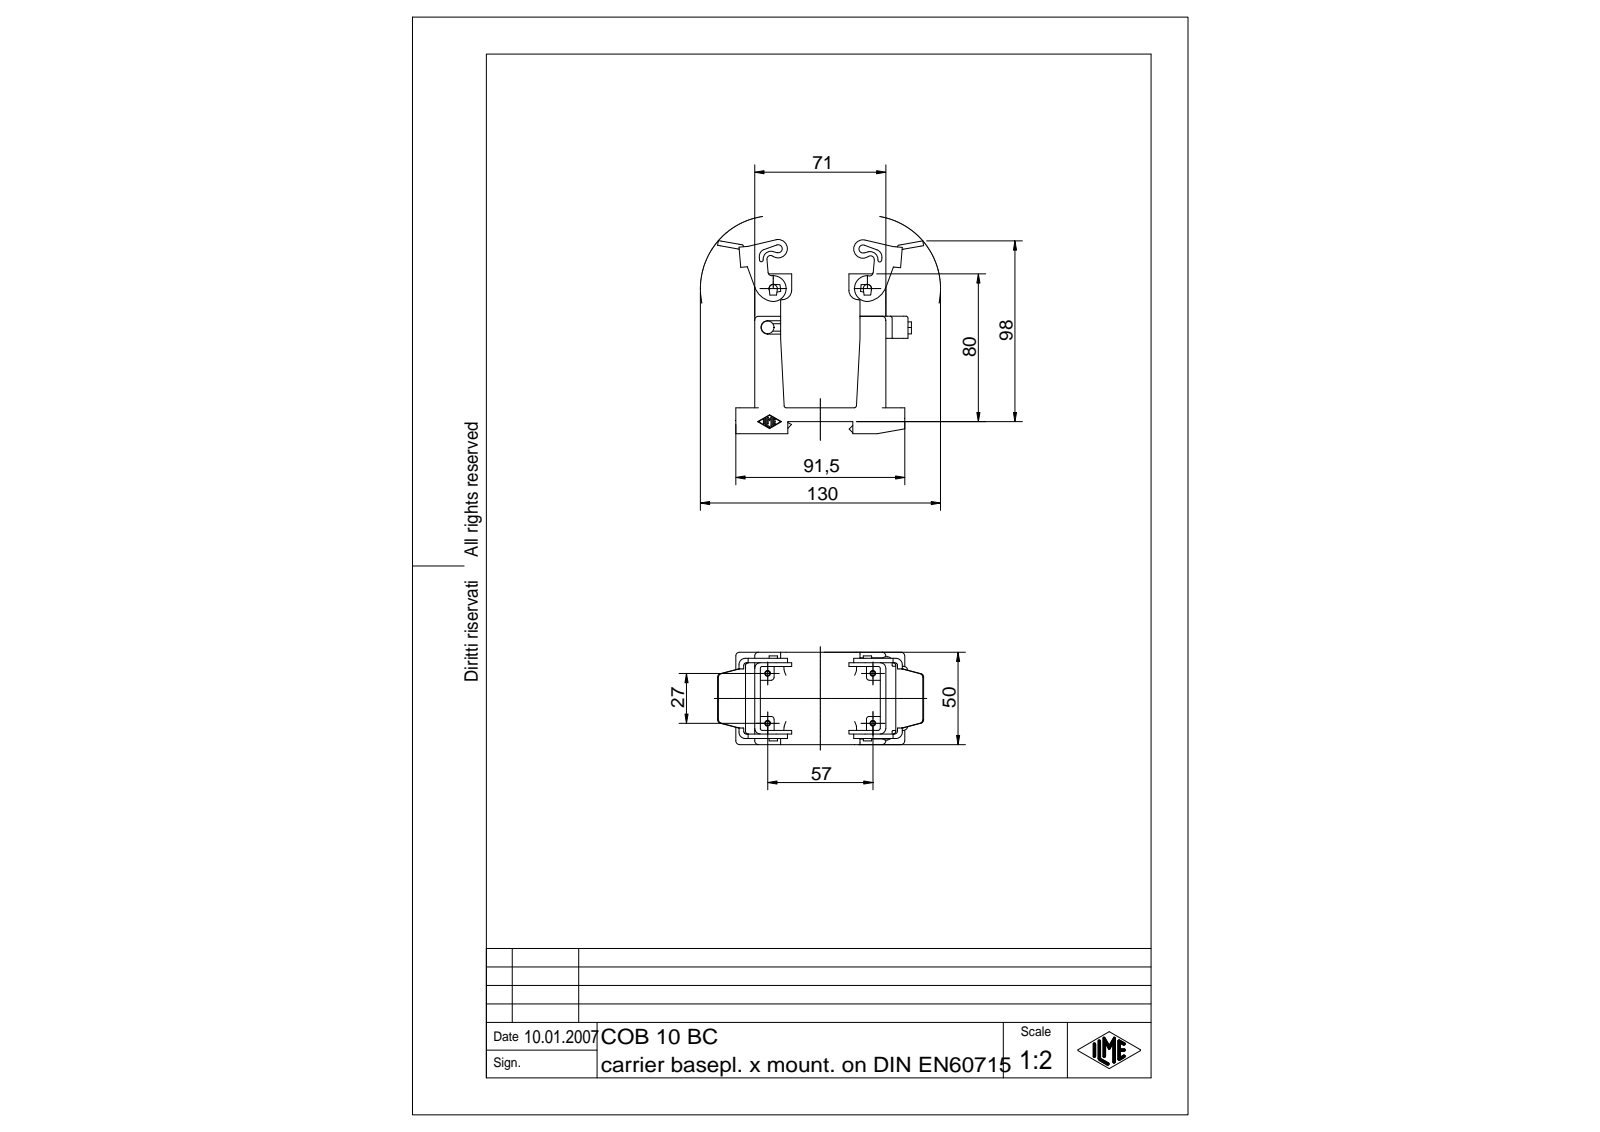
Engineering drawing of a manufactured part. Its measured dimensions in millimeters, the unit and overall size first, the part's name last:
Units: millimetres
Overall size (bounding box): 111.6 × 105.07 × 50
Round bosses / shafts (diameter × count): ⌀7 ×1, ⌀4.5 ×1, ⌀4 ×1
Partial cylindrical surfaces — rounded edges, fillets, slot ends (radius × count): R2 ×22, R1 ×18, R0.25 ×14, R1.5 ×8, R5 ×5, R0.5 ×4, R2.5 ×4, R3 ×4
Main face-to-face distances: 7.5, 14, 50, 6.5, 2, 3, 68, 7.7, 42.3, 5.7
Volume: 98 227 mm³ · Surface area: 40 344 mm²
Bodies: 1 solid, 534 faces (228 planar, 191 cylindrical, 115 other)
Part name (STEP PRODUCT): Einsatzhalter für die Montage auf DIN Schiene
STEP written by: Autodesk Inventor 7 (AUTOMOTIVE_DESIGN)
